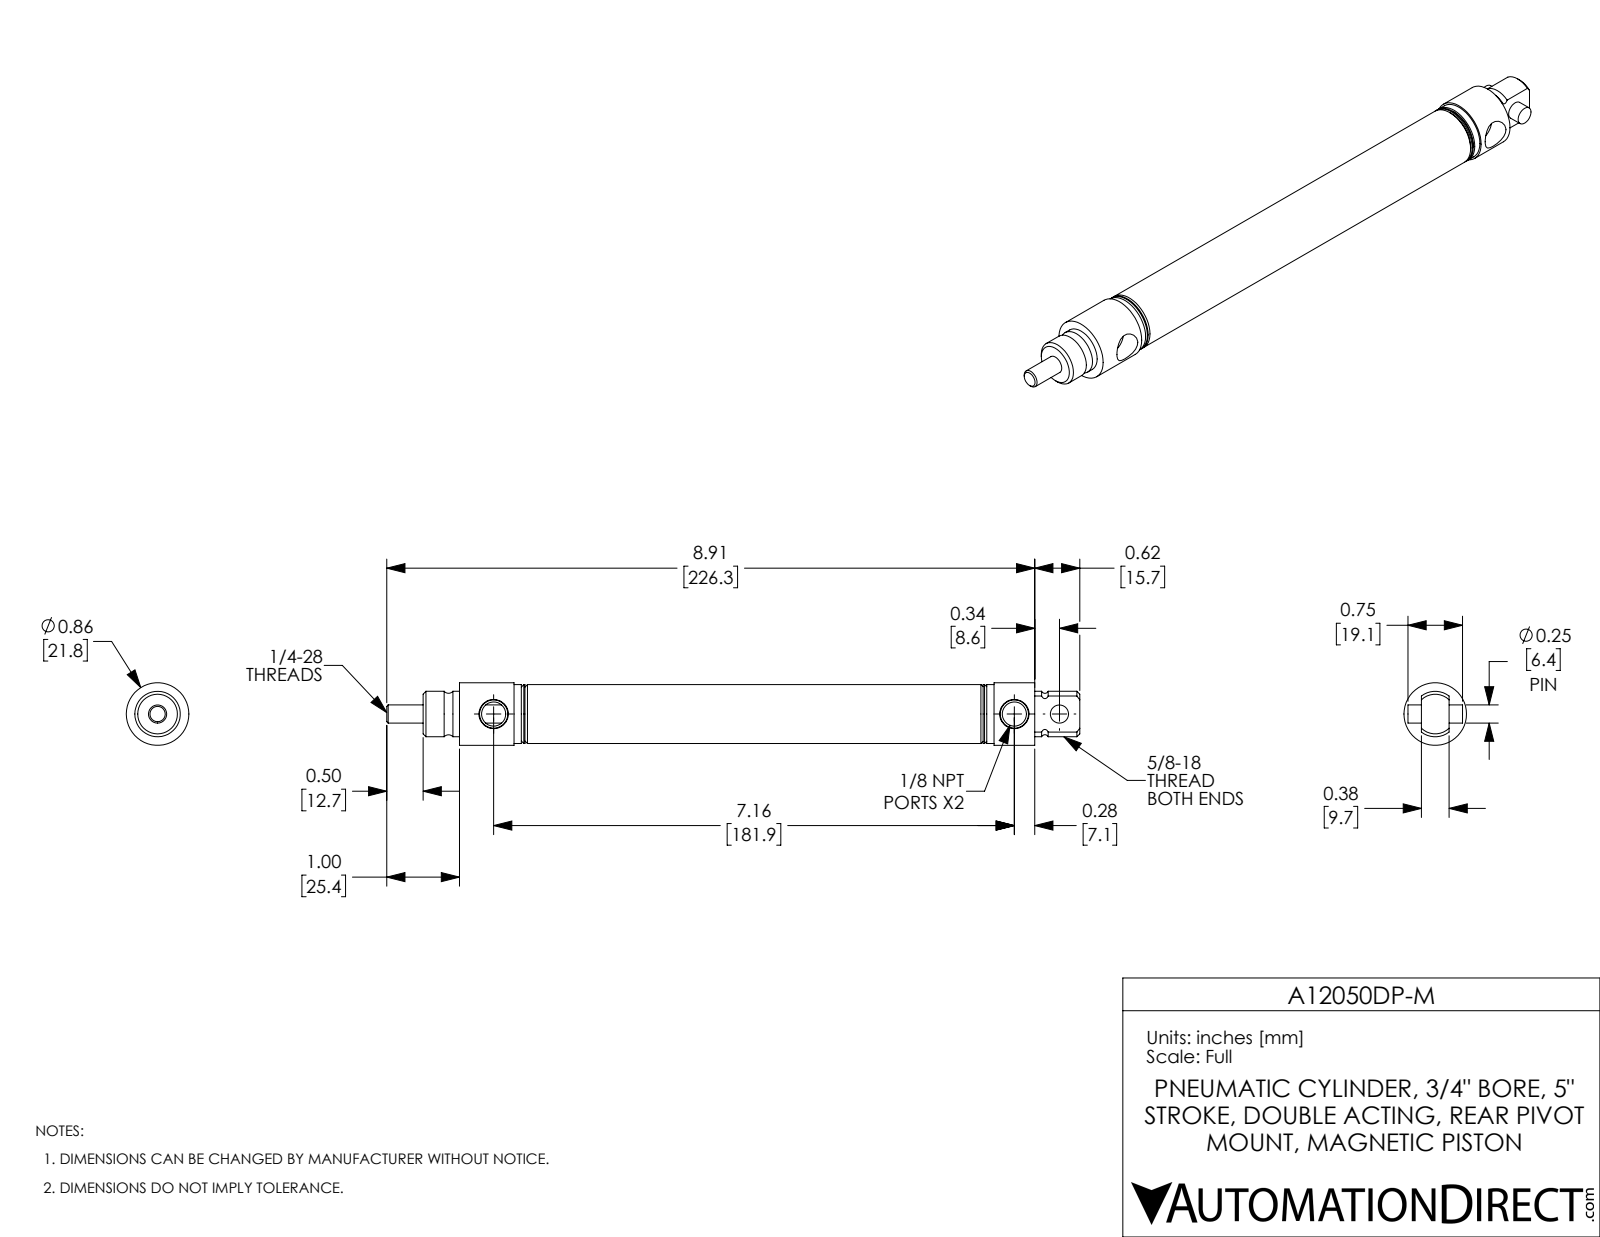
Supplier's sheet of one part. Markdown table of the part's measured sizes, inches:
| quantity | value |
| --- | --- |
| part name | A12050DP-M-MainBody; A12050DP-M; A12050DP-M-PIN; A12050DP-M-Rod |
| STEP written by | SolidWorks 2017 (AUTOMOTIVE_DESIGN) |
| units | inches |
| bodies | 3 solids, 91 faces (21 planar, 38 cylindrical, 32 other) |
| overall size | 9.53 × 0.86 × 0.86 |
| volume | 2.429 in³ |
| surface area | 48.53 in² |
| round holes (diameter × count) | 0.25 × 2, 0.332 × 2, 0.75 × 1 |
| round bosses / shafts (diameter × count) | 0.86 × 1, 0.81 × 1, 0.625 × 1 |
| main face-to-face distances | 0.5, 6.705, 5.5, 5, 1.205, 1.705, 6.705, 7.91, 6.205, 1.205 |
| hole center spacings | 0.62, 7.16, 7.78 |
